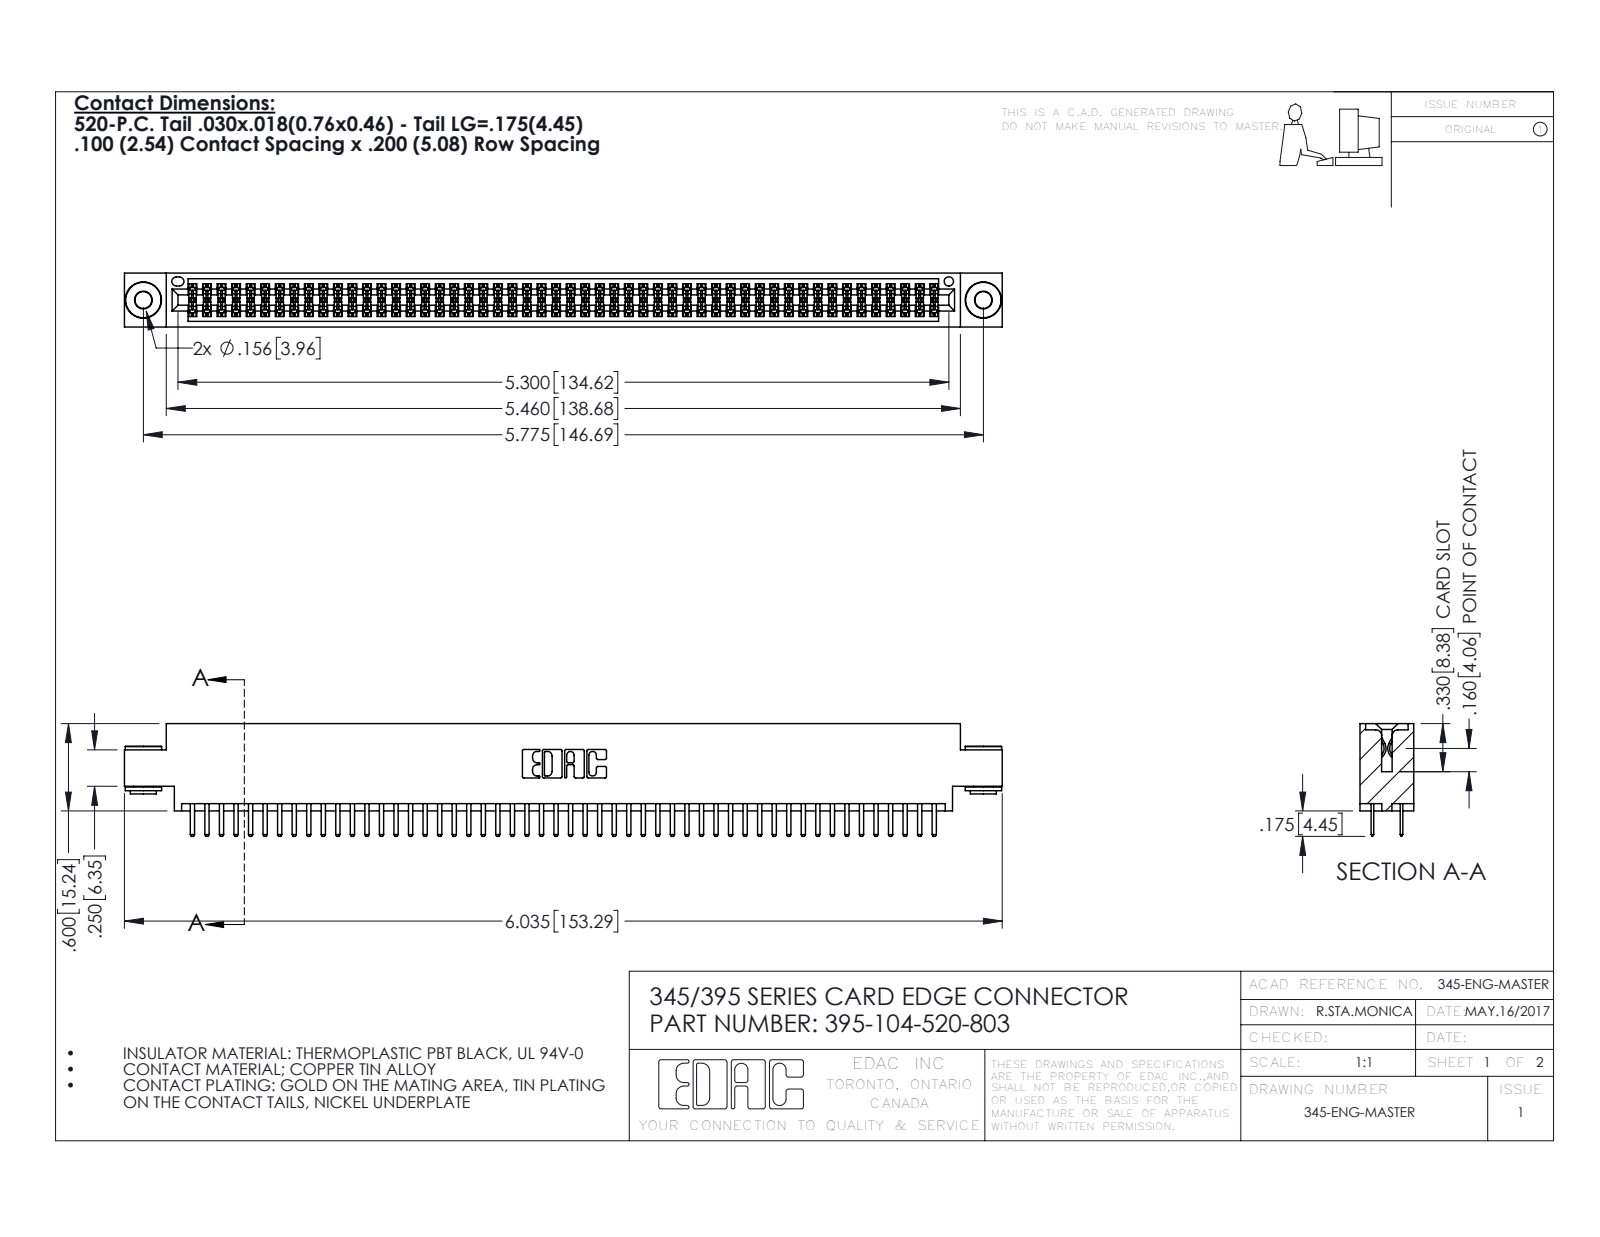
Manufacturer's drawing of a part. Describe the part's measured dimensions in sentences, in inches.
The part is named "345 Part_0.170 Offset - 0.156 Dia-TH; 395-104-520-803; 345-250-002_345-250-002-102; 345-292-001_345-293-120". Its 3-D file was written by "SolidWorks 2016 (CONFIG_CONTROL_DESIGN)". It is 107 solids with 5784 faces: 3734 planar, 2042 cylindrical and 8 other. Overall it measures 6.035 by 0.775 by 0.37 inches. Its volume is 0.906 cubic inches and its surface area 34.7 square inches. Round holes: 2 of diameter 0.116, 2 of diameter 0.156, 1 of diameter 0.064. Round bosses or shafts: 2 of diameter 0.25, 2 of diameter 0.18, 2 of diameter 0.136. Partial cylindrical surfaces (rounded edges, fillets, slot ends): 156 of radius 0.006, 108 of radius 0.01, 22 of radius 0.01, 6 of radius 0.007, 6 of radius 0.031, 3 of radius 0.026, 2 of radius 0.014, 2 of radius 0.019. The main face-to-face distances are 0.072, 0.298, 0.2, 0.37, 0.098, 0.272, 0.025, 0.225, 0.022, 0.175. The hole center spacings are 0.27, 5.539, 5.775.
